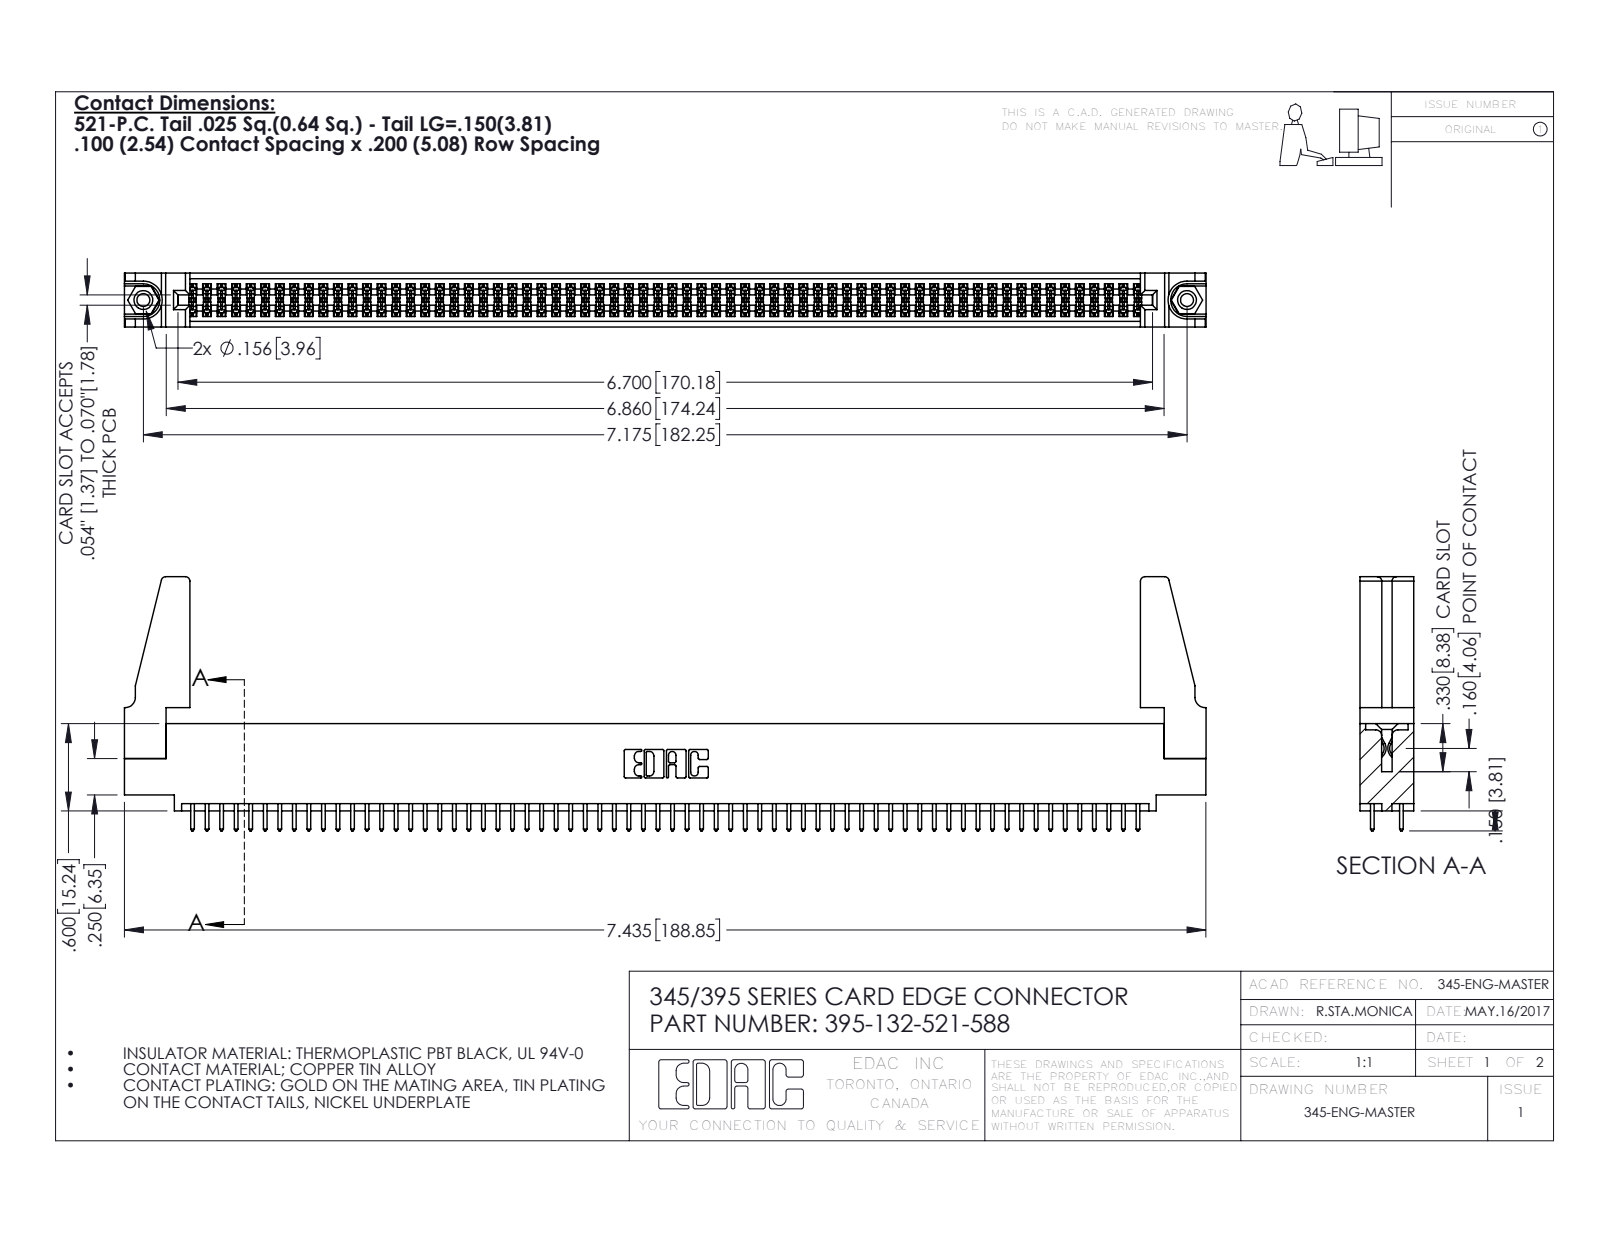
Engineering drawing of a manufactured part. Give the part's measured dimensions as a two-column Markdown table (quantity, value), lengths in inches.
| quantity | value |
| --- | --- |
| part name | 395-132-521-588; 345-250-001_345-250-001-102; 345-220-078_345-220-088; 345-292-001_345-293-121 (+1 more) |
| STEP written by | SolidWorks 2016 (CONFIG_CONTROL_DESIGN) |
| units | inches |
| bodies | 137 solids, 6854 faces (4512 planar, 2326 cylindrical, 16 other) |
| overall size | 7.436 × 1.747 × 0.37 |
| volume | 1.324 in³ |
| surface area | 47.42 in² |
| round holes (diameter × count) | 0.089 × 2, 0.125 × 2, 0.156 × 2, 0.064 × 1 |
| round bosses / shafts (diameter × count) | 0.155 × 2 |
| partial cylindrical surfaces (radius × count) | 0.006 × 198, 0.01 × 132, 0.01 × 22, 0.03 × 8, 0.007 × 6, 0.031 × 6, 0.026 × 3, 0.014 × 2 |
| main face-to-face distances | 0.072, 0.298, 0.37, 0.098, 0.272, 0.025, 0.2, 0.225, 0.175, 0.149 |
| hole center spacings | 0.27, 6.939, 7.175 |
